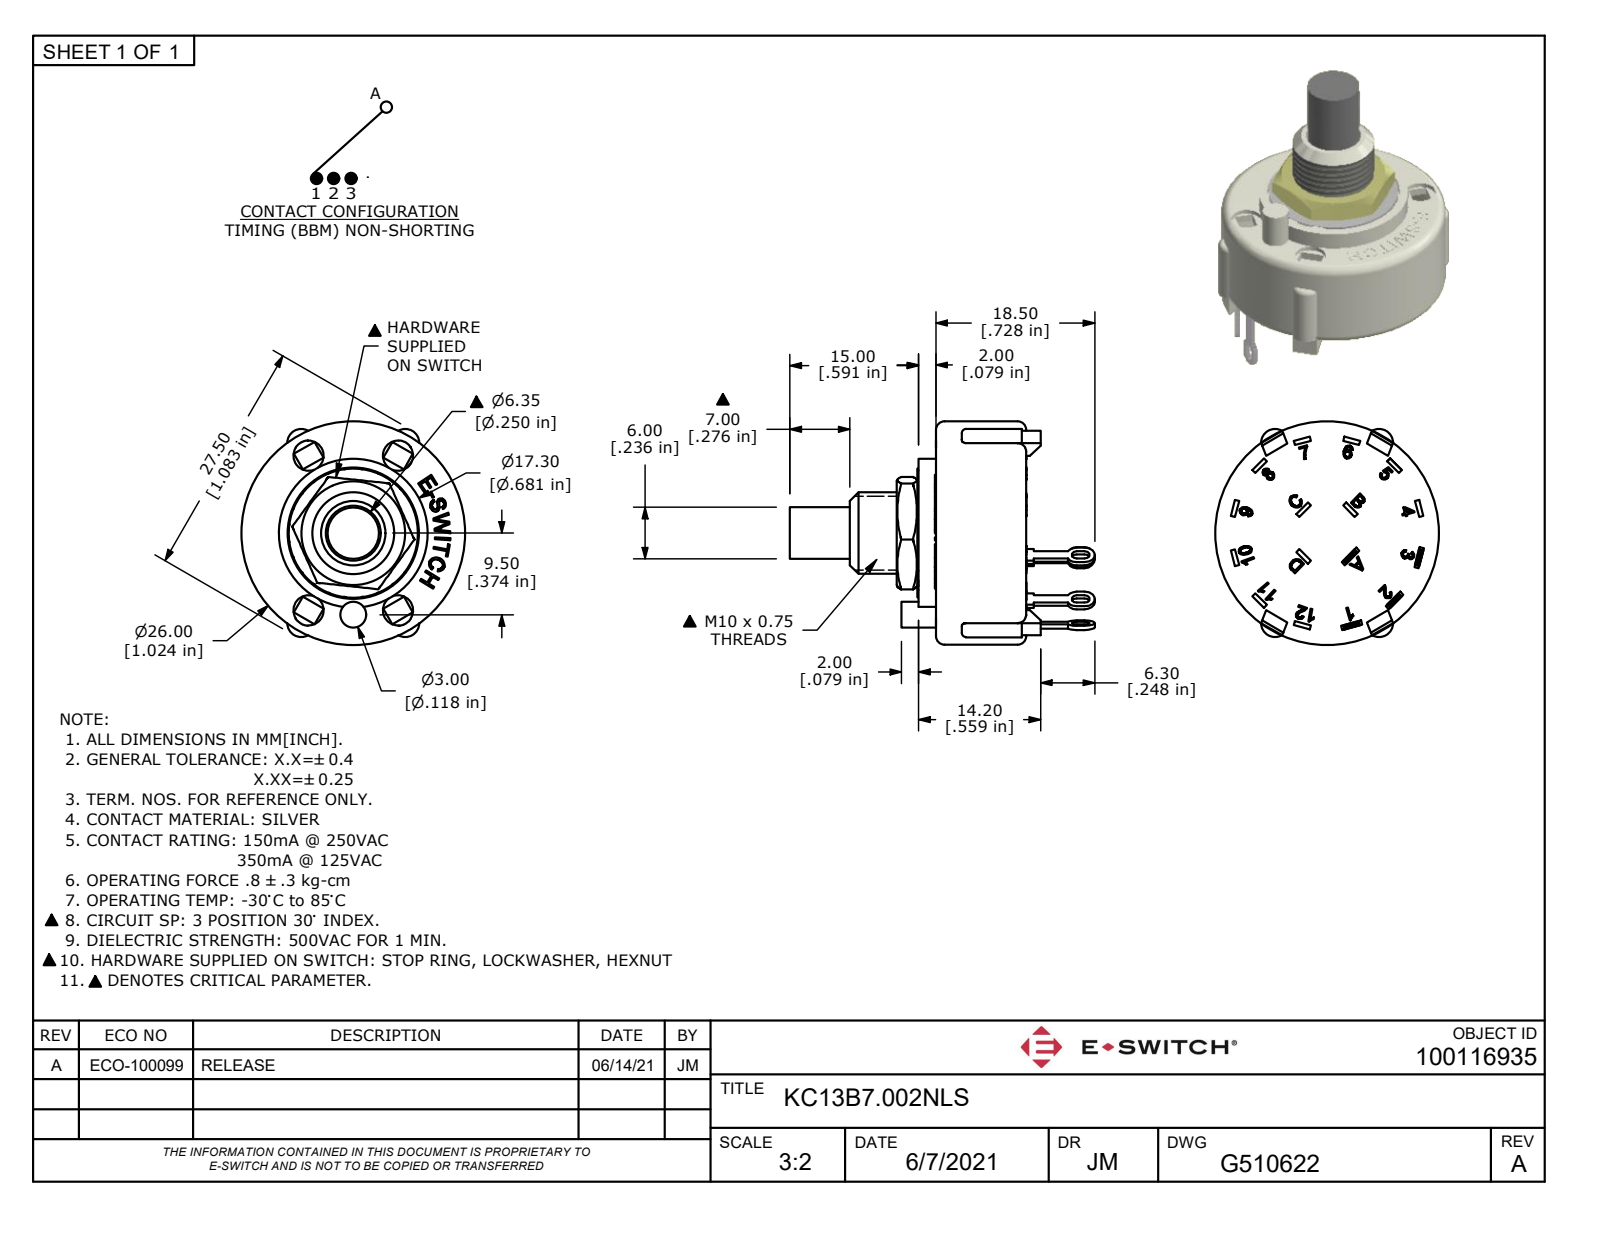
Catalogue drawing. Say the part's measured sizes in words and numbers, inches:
The part is named "KC13B7.002NLS". Its 3-D file was written by "Autodesk Inventor 2012 (CONFIG_CONTROL_DESIGN)". It is 2 solids with 670 faces: 440 planar, 48 cylindrical and 182 other. Overall it measures 1.398 by 1.024 by 1.024 inches. Its volume is 0.195 cubic inches and its surface area 7.649 square inches. Round holes: 4 of diameter 0.14, 1 of diameter 0.25, 1 of diameter 0.404, 1 of diameter 0.406, 1 of diameter 0.602, 1 of diameter 0.945, 1 of diameter 1.024. Round bosses or shafts: 1 of diameter 0.681, 1 of diameter 0.591, 1 of diameter 0.374, 1 of diameter 0.236, 1 of diameter 0.118. Partial cylindrical surfaces (rounded edges, fillets, slot ends): 6 of radius 0.024, 6 of radius 0.047, 4 of radius 0.065, 2 of radius 0.008, 1 of radius 0.043, 1 of radius 0.287. The main face-to-face distances are 0.039, 0.319, 0.358, 0.413, 0.374, 0.055, 0.14, 0.02, 0.453, 0.079. The hole center spacings are 0.409, 0.709, 0.819.
